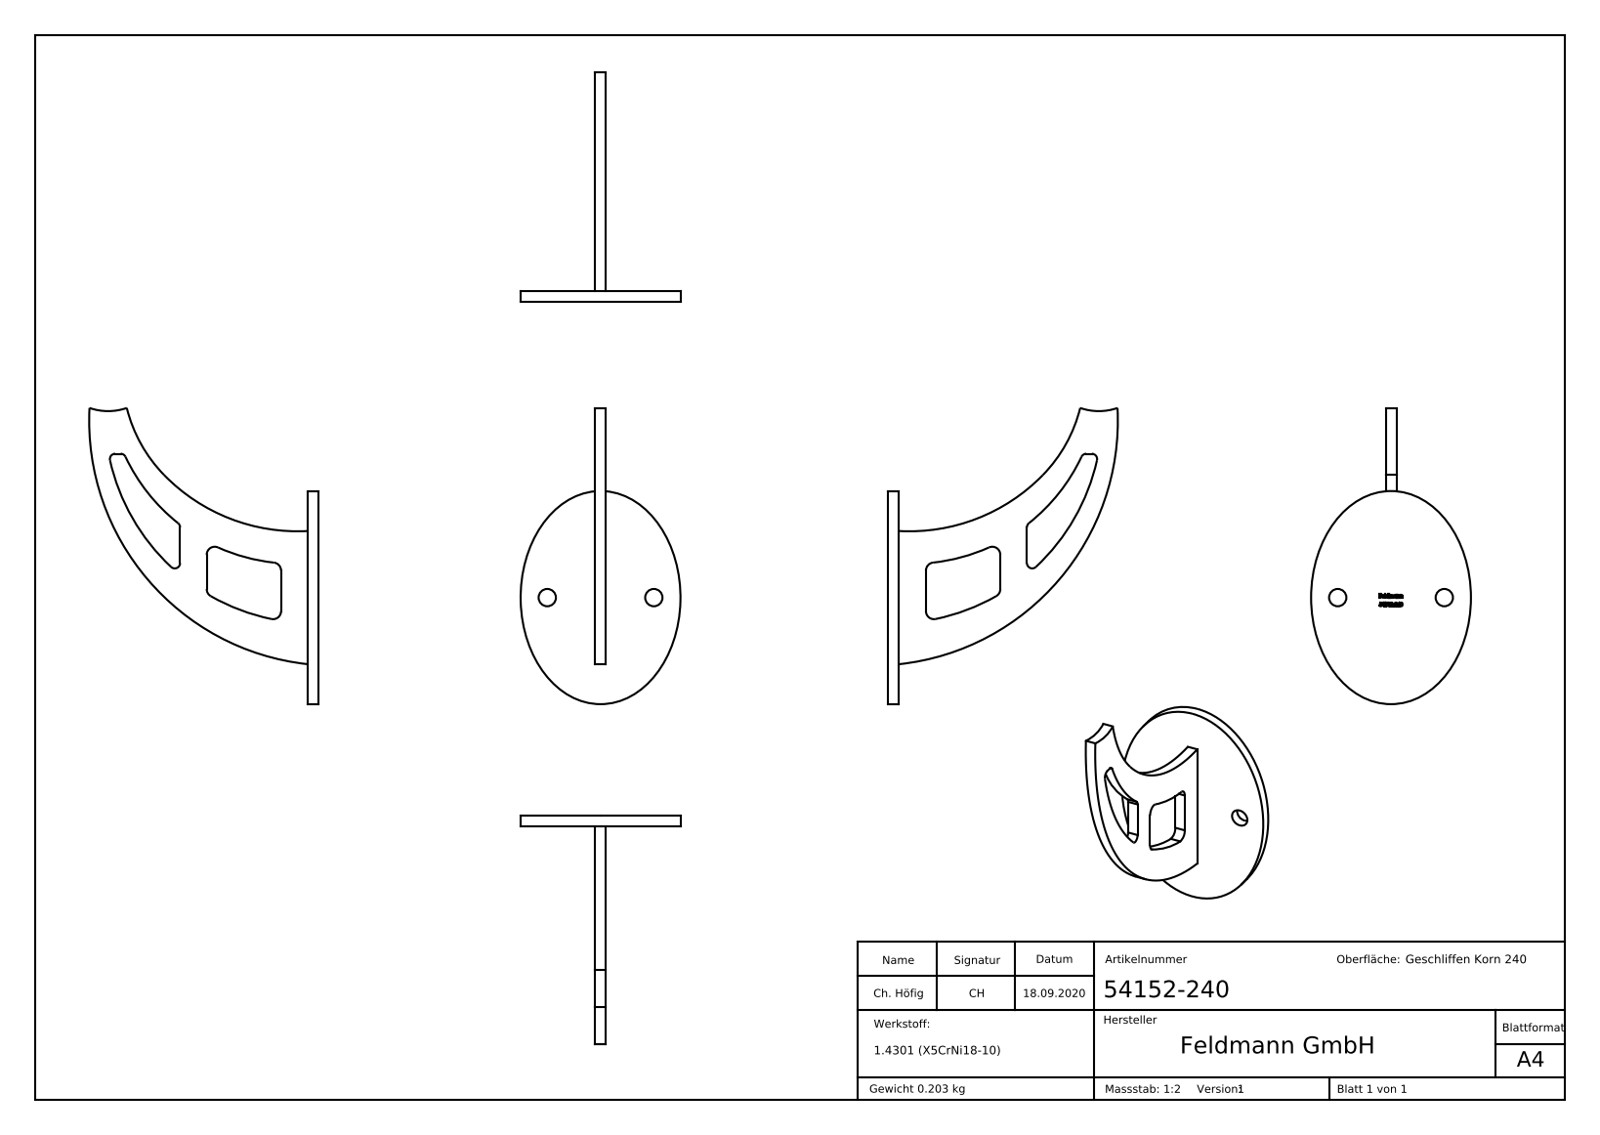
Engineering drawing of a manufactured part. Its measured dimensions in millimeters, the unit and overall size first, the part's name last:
Units: millimetres
Overall size (bounding box): 111.19 × 86.12 × 60
Round holes (diameter × count): ⌀6.5 ×2
Partial cylindrical surfaces — rounded edges, fillets, slot ends (radius × count): R2 ×4, R3 ×4, R70 ×2, R21.2 ×1, R55 ×1, R78.5 ×1, R92 ×1
Main face-to-face distances: 4, 14.1, 10.1, 52, 48, 37.9, 42, 38, 27.9, 10
Hole centre spacings: 40
Volume: 25 748 mm³ · Surface area: 15 502 mm²
Bodies: 1 solid, 252 faces (145 planar, 20 cylindrical, 87 other)
Part name (STEP PRODUCT): 54152-240
STEP written by: SolidWorks 2018 (CONFIG_CONTROL_DESIGN)
